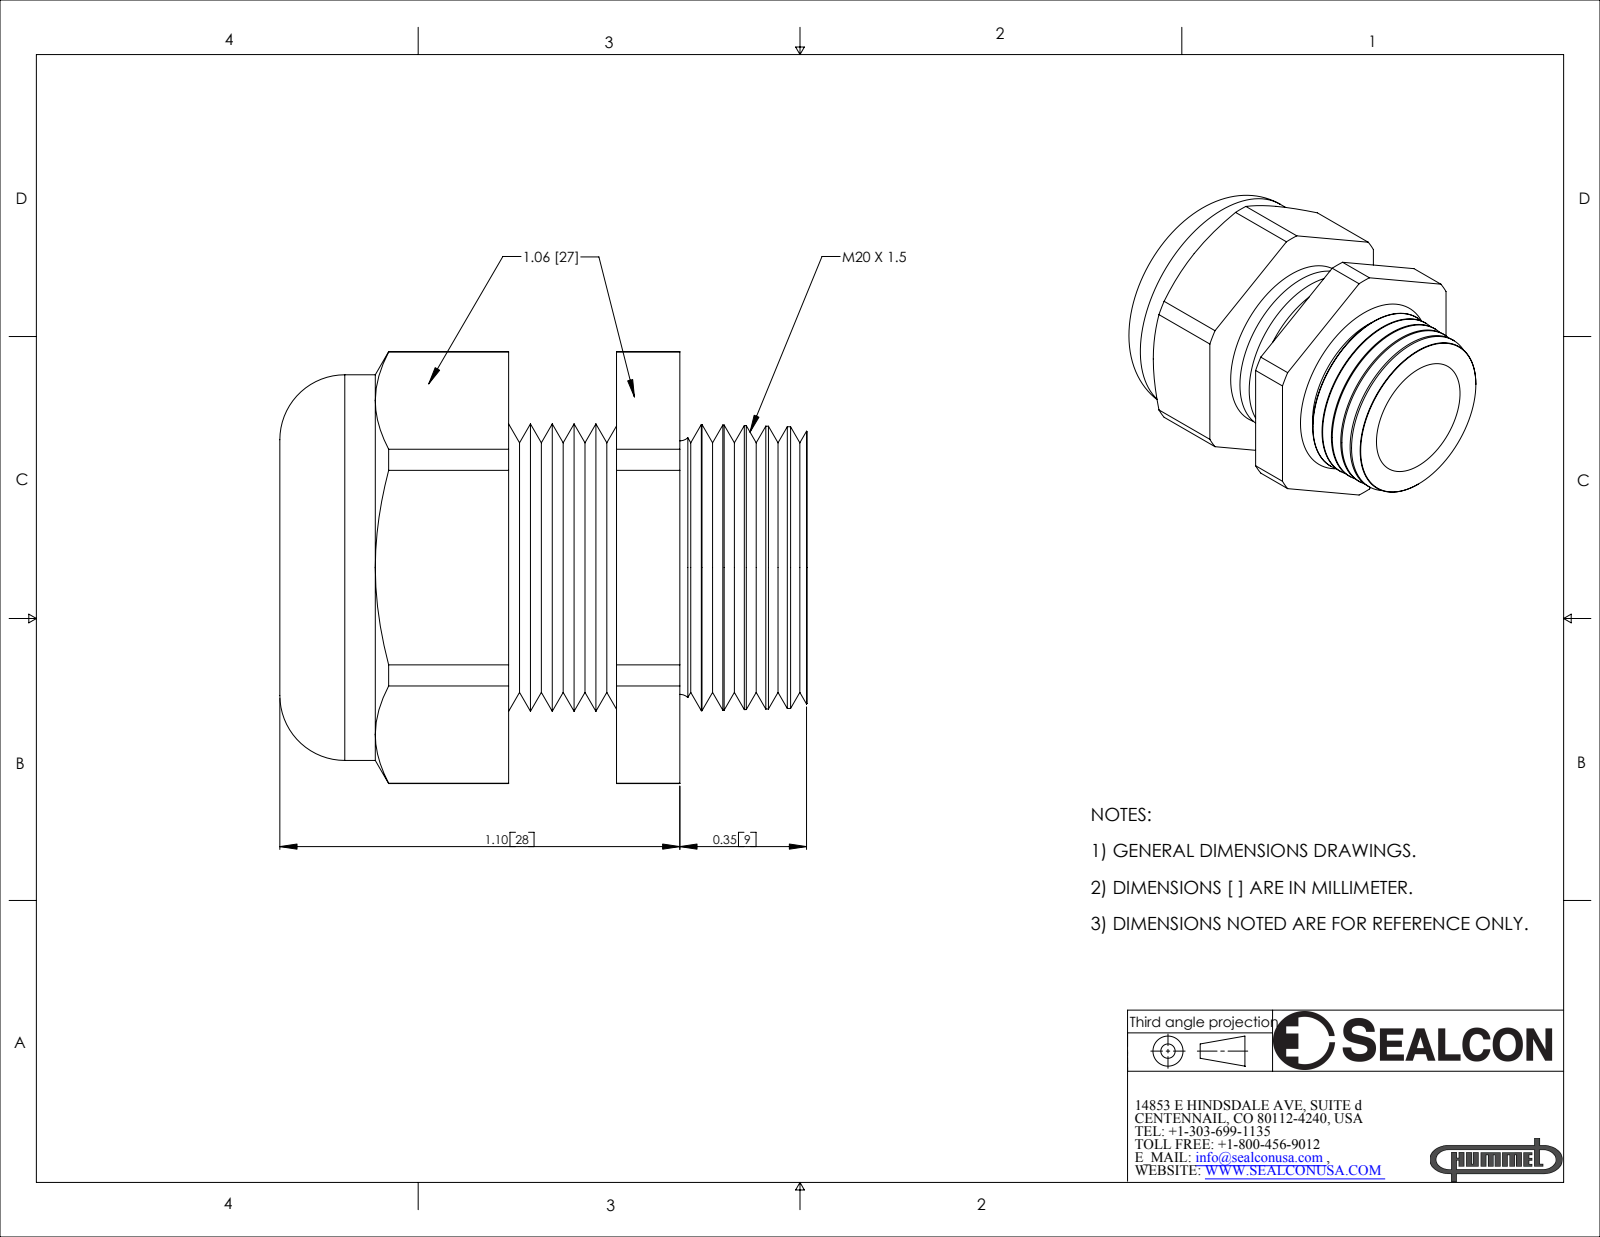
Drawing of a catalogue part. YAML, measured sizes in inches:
part_name: "CD22MR"
step_written_by: "SolidWorks 2007 (CONFIG_CONTROL_DESIGN)"
units: inches
bodies: {solids: 2, faces: 116, planar: 20, cylindrical: 24, other: 72}
overall_size: [1.45, 1.187, 1.06]
volume: 0.725
surface_area: 11.64
round_holes:
  - {diameter: 0.47, count: 1}
  - {diameter: 0.671, count: 1}
  - {diameter: 0.79, count: 1}
round_bosses_or_shafts:
  - {diameter: 1.06, count: 1}
partial_cylinders:
  - {radius: 0.594, count: 1}
face_to_face_distances: [1.06, 0.297, 0.471, 0.174, 0.367, 0.663, 0.837, 1.187, 0.821, 0.524]
